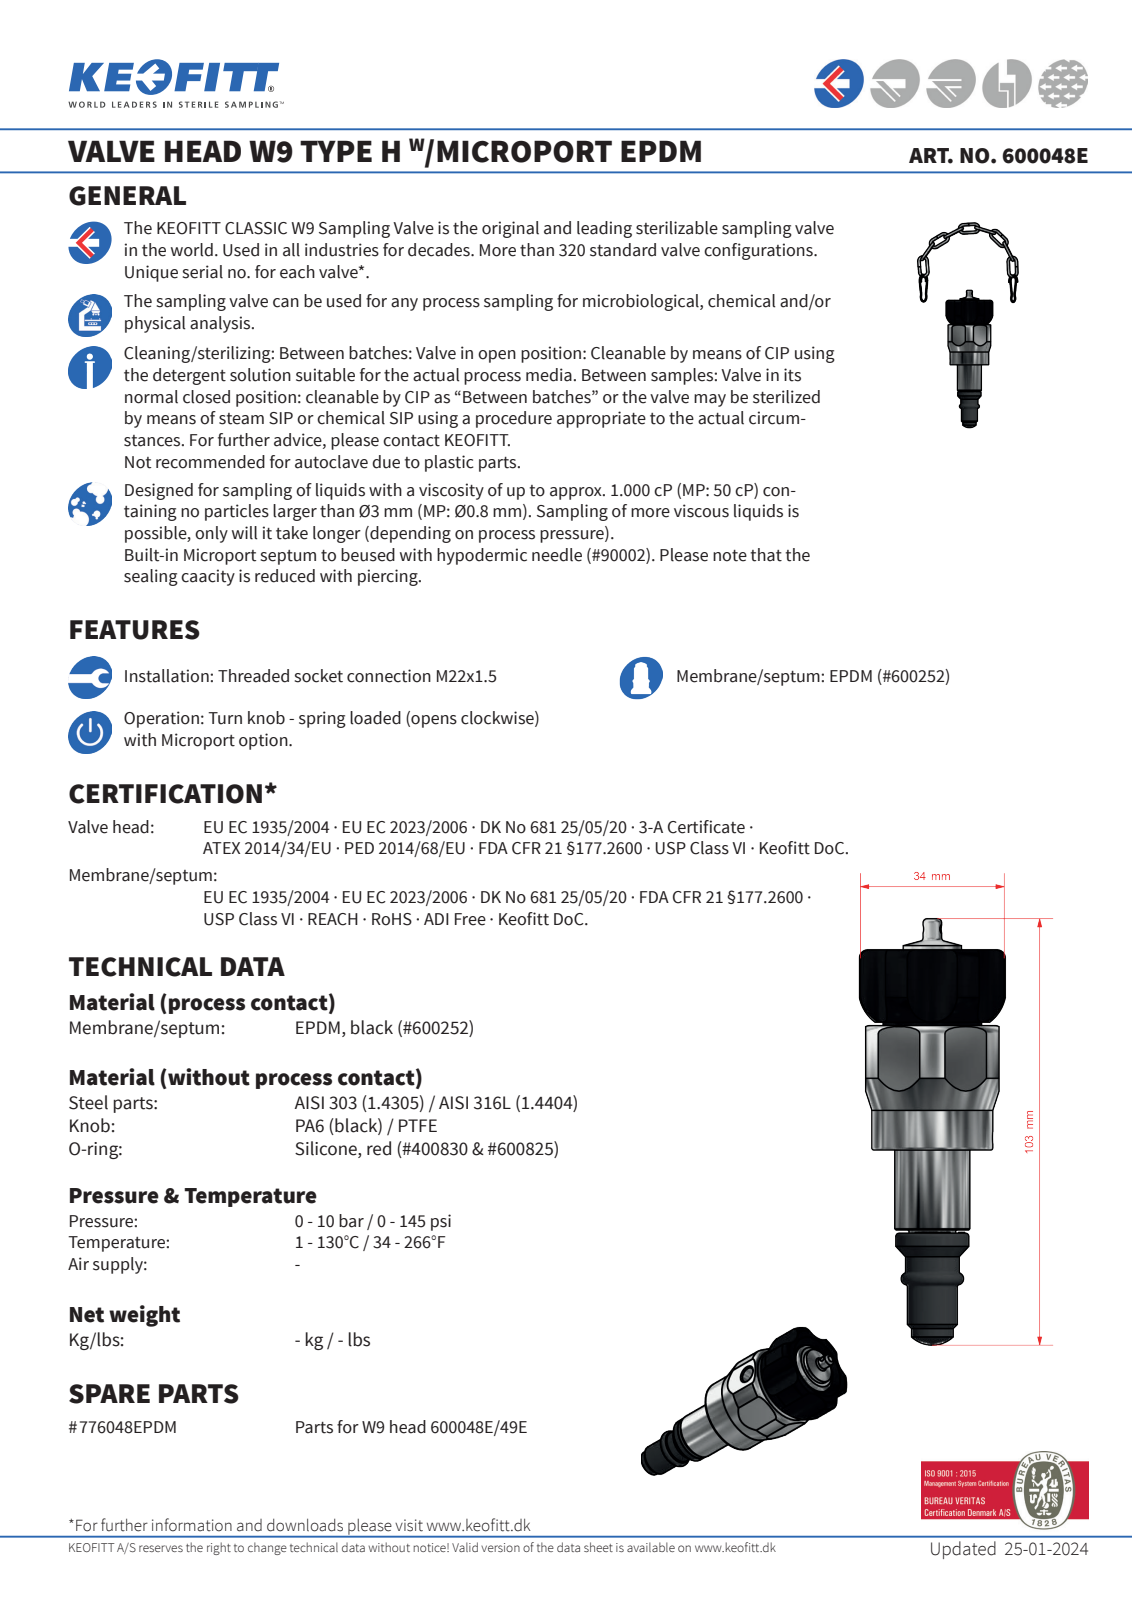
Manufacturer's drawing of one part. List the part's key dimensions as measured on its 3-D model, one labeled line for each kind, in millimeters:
Part name (STEP PRODUCT): 600048E
STEP written by: Autodesk Inventor 2022 (AUTOMOTIVE_DESIGN)
Units: millimetres
Bodies: 1 solid, 241 faces (97 planar, 27 cylindrical, 117 other)
Overall size (bounding box): 103 × 34.91 × 34.82
Volume: 45 846 mm³ · Surface area: 9 501 mm²
Round bosses / shafts (diameter × count): ⌀29 ×1, ⌀23.6 ×1, ⌀18 ×1, ⌀17.5 ×1, ⌀14 ×1, ⌀12.9 ×1, ⌀12 ×1, ⌀10 ×1
Partial cylindrical surfaces — rounded edges, fillets, slot ends (radius × count): R8 ×6, R17 ×1, R17.5 ×1
Main face-to-face distances: 32, 48.5, 30, 18.5, 31.04, 1.04, 17.46, 19.8, 49.8, 50.84
